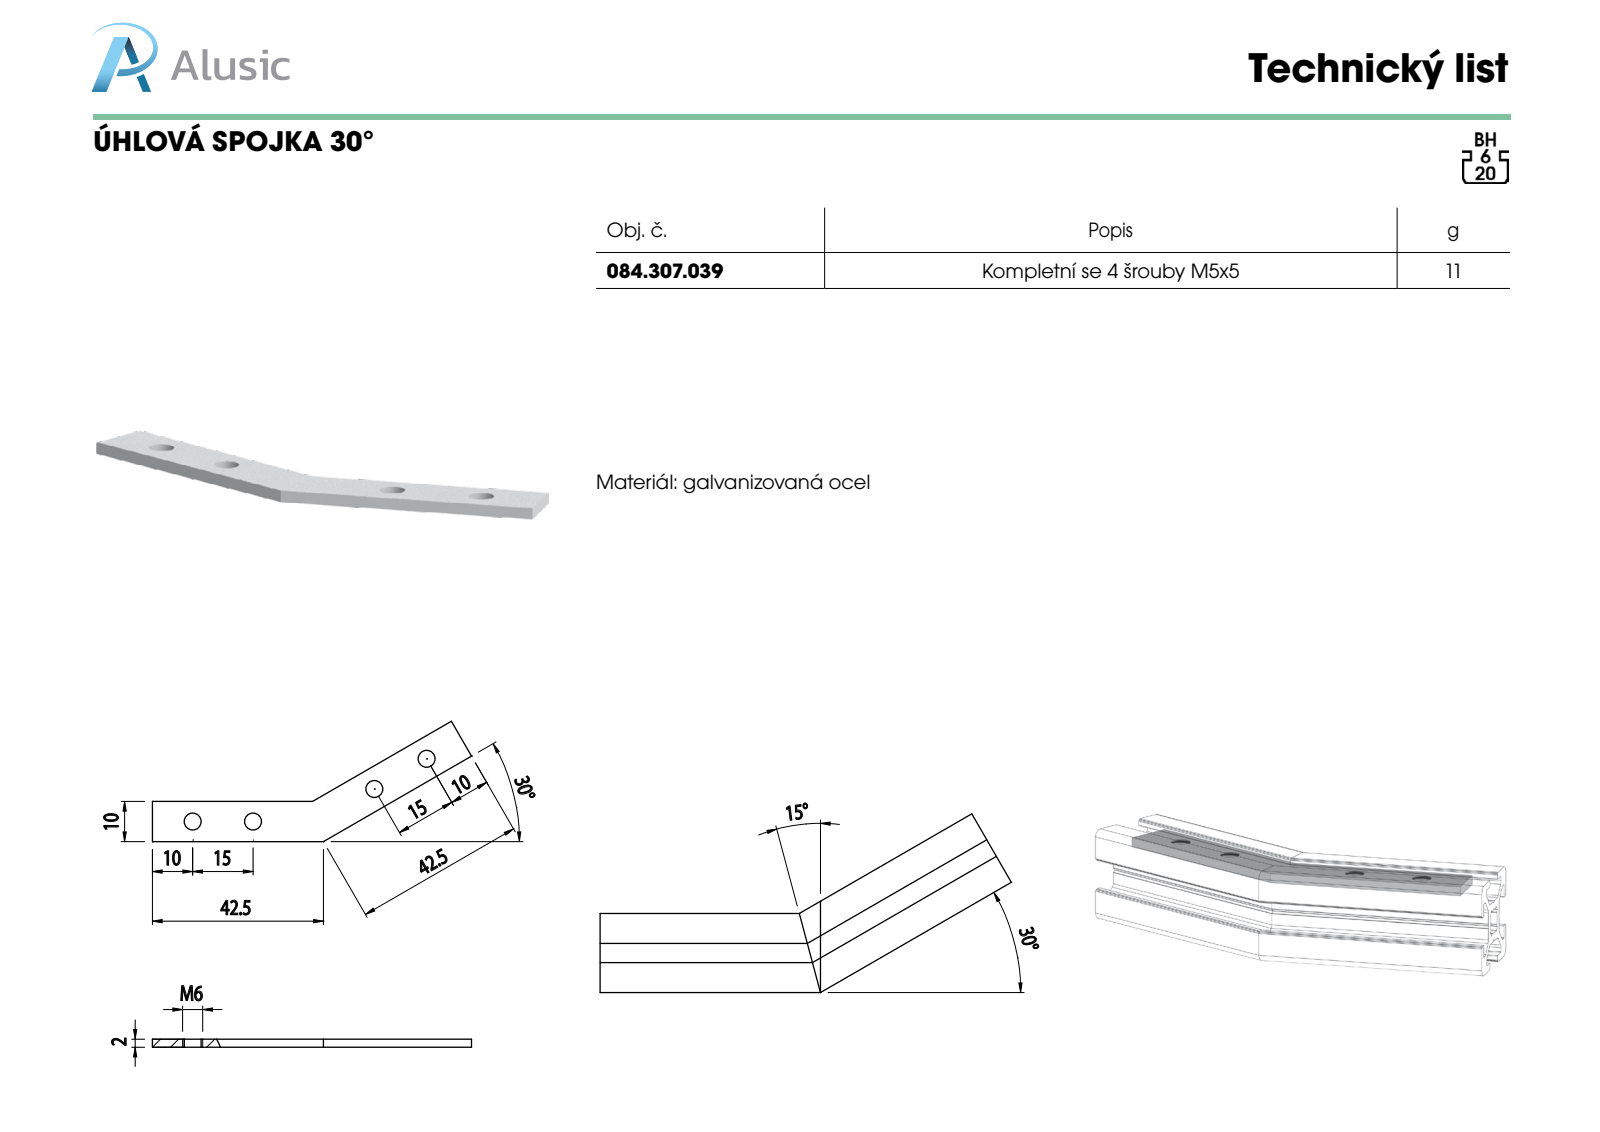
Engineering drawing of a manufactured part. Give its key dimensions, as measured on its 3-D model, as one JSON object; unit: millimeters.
{"part_name": "084.307.039", "step_written_by": "SolidWorks 2012 (CONFIG_CONTROL_DESIGN)", "units": "millimeters", "bodies": {"solids": 1, "faces": 16, "planar": 8, "cylindrical": 8, "other": 0}, "overall_size": [79.31, 29.91, 2], "volume_mm3": 1536, "surface_area_mm2": 2010, "round_holes": [[4.2, 4]], "face_to_face_distances": [2, 10], "hole_center_spacings": [15, 45.88, 31.22, 60.2]}
